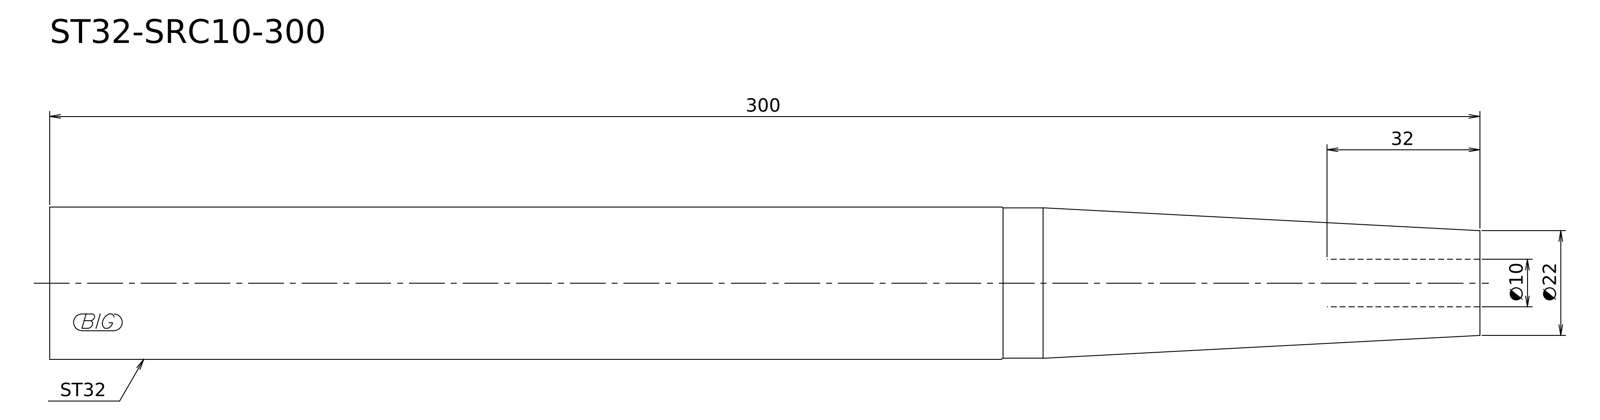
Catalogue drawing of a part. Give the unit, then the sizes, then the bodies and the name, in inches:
Units: inches
Overall size (bounding box): 11.811 × 1.26 × 1.26
Round bosses / shafts (diameter × count): ⌀1.26 ×1, ⌀1.244 ×1
Main face-to-face distances: 11.811
Volume: 13.4 in³ · Surface area: 46.27 in²
Bodies: 1 solid, 6 faces (2 planar, 2 cylindrical, 2 other)
STEP written by: Kubotek KeyCreator V8.5.1 (14335) (CONFIG_CONTROL_DESIGN)
